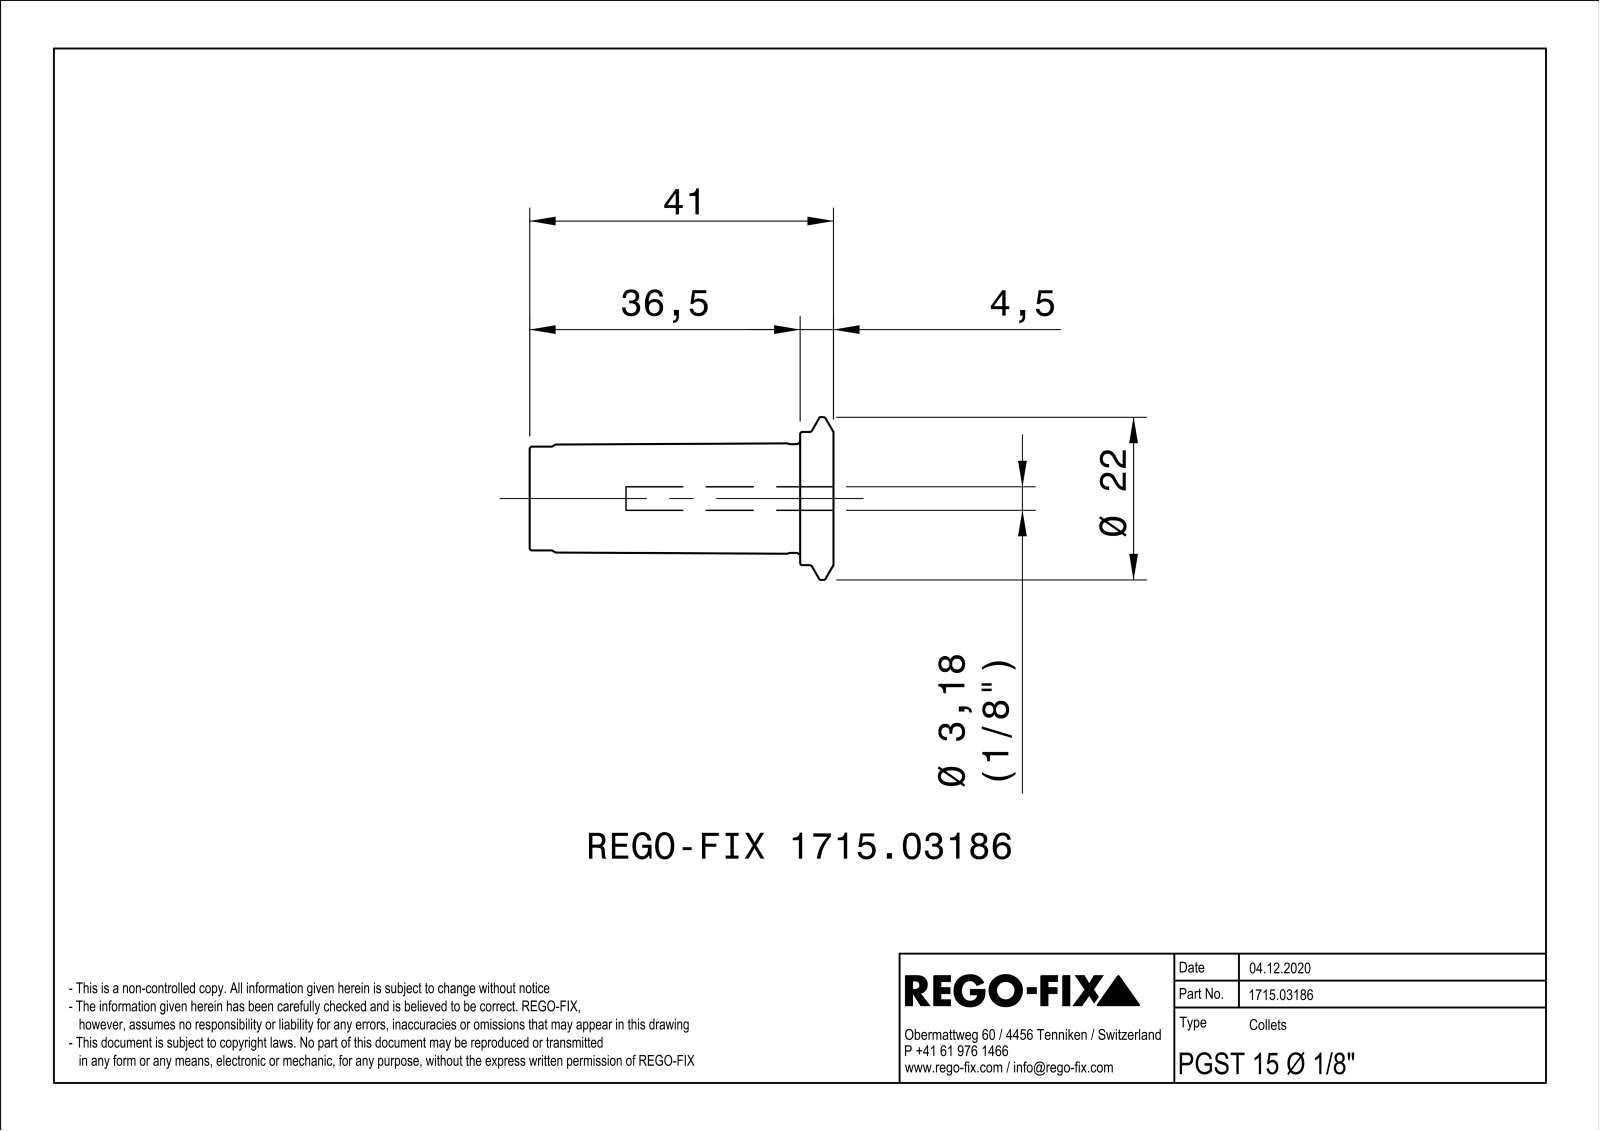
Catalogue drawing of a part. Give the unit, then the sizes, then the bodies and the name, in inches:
Units: inches
Overall size (bounding box): 1.614 × 0.865 × 0.865
Round holes (diameter × count): ⌀0.059 ×4, ⌀0.118 ×1, ⌀0.125 ×1, ⌀0.295 ×1, ⌀0.394 ×1, ⌀0.451 ×1, ⌀0.492 ×1
Round bosses / shafts (diameter × count): ⌀0.865 ×1, ⌀0.709 ×1, ⌀0.579 ×1, ⌀0.551 ×1, ⌀0.472 ×1, ⌀0.437 ×1, ⌀0.197 ×1, ⌀0.11 ×1
Main face-to-face distances: 0.177, 1.437, 1.614, 1.26, 1.102, 0.925, 0.335, 0.512, 0.035, 1.142
Hole centre spacings: 0.157, 0.273, 0.272
Volume: 0.427 in³ · Surface area: 5.887 in²
Bodies: 2 solids, 56 faces (14 planar, 18 cylindrical, 24 other)
Part name (STEP PRODUCT): NOCUT
STEP written by: SIEMENS PLM Software Solid Edge ST10 (AUTOMOTIVE_DESIGN)
